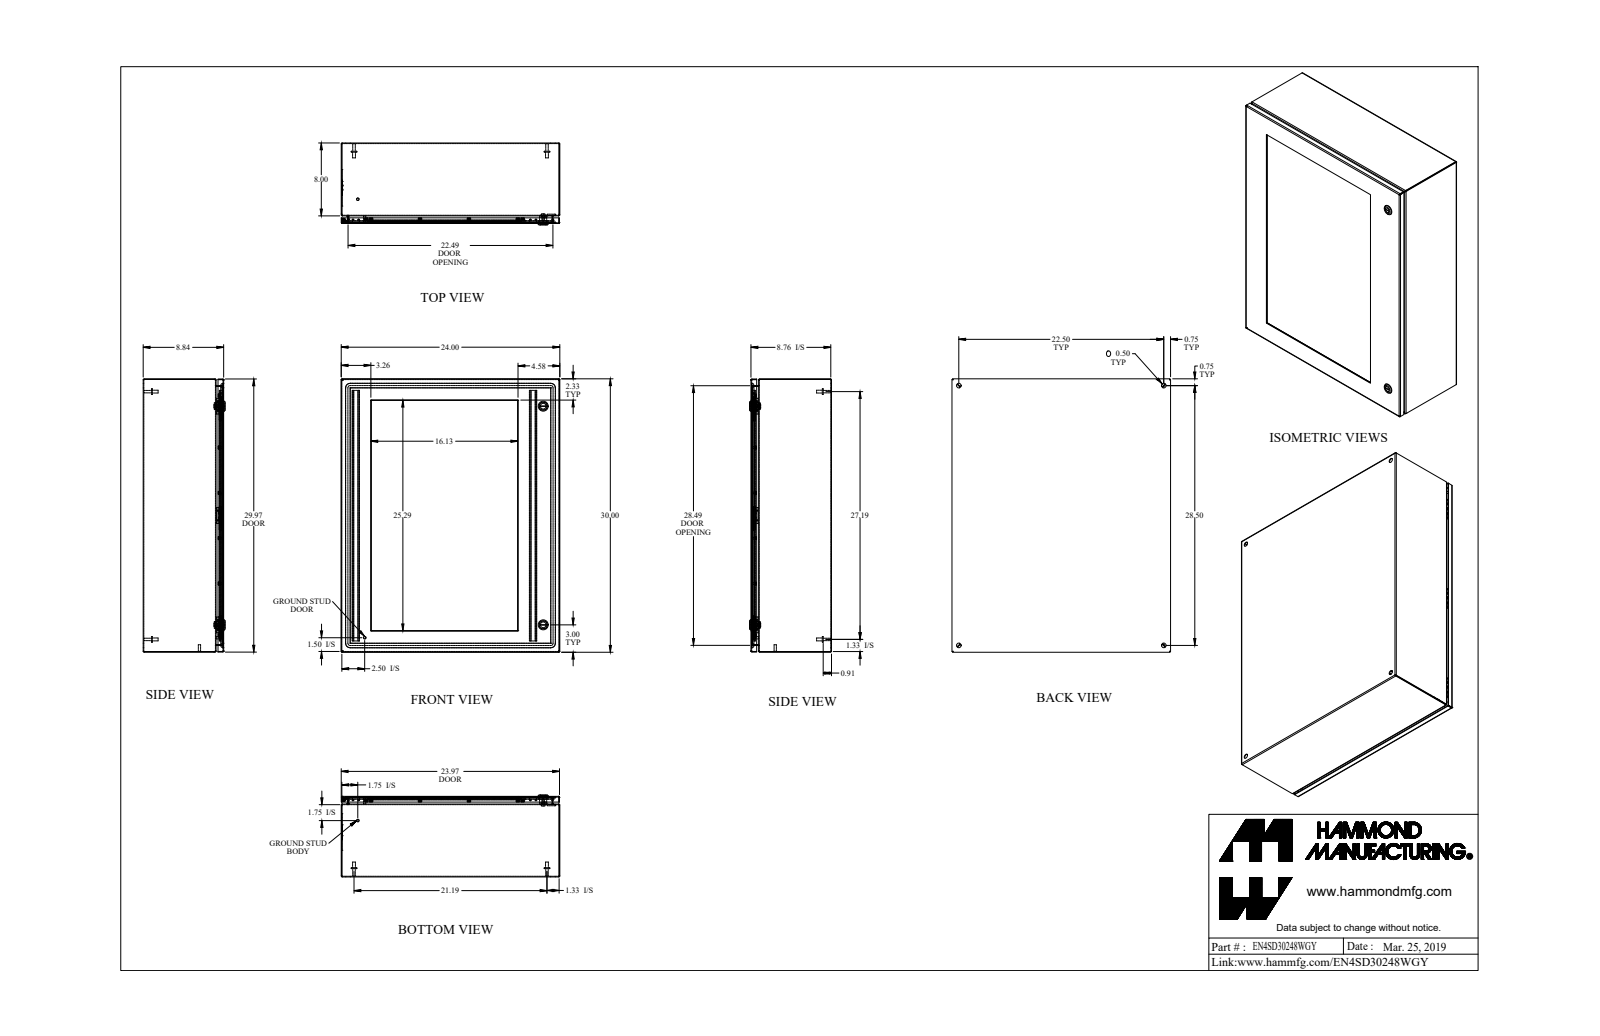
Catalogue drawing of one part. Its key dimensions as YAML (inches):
part_name: "EN4SD30248WGY_Default"
step_written_by: "SolidWorks 2019 (CONFIG_CONTROL_DESIGN)"
units: inches
bodies: {solids: 80, faces: 1652, planar: 833, cylindrical: 511, other: 308}
overall_size: [30, 24, 8.997]
volume: 281.4
surface_area: 5826
round_holes:
  - {diameter: 0.13, count: 20}
  - {diameter: 0.25, count: 20}
  - {diameter: 0.5, count: 4}
  - {diameter: 0.232, count: 2}
  - {diameter: 0.625, count: 2}
  - {diameter: 0.785, count: 2}
  - {diameter: 0.172, count: 1}
  - {diameter: 0.24, count: 1}
  - {diameter: 0.242, count: 1}
round_bosses_or_shafts:
  - {diameter: 0.226, count: 21}
  - {diameter: 0.368, count: 20}
  - {diameter: 0.164, count: 20}
  - {diameter: 0.625, count: 4}
  - {diameter: 0.313, count: 4}
  - {diameter: 0.27, count: 4}
  - {diameter: 1.1, count: 2}
  - {diameter: 0.525, count: 2}
partial_cylinders:
  - {radius: 0.036, count: 20}
  - {radius: 0.108, count: 20}
  - {radius: 0.043, count: 12}
  - {radius: 0.081, count: 12}
  - {radius: 0.125, count: 12}
  - {radius: 0.382, count: 12}
  - {radius: 19.003, count: 8}
  - {radius: 0.006, count: 6}
face_to_face_distances: [0.072, 8.765, 8.693, 8.443, 0.25, 8.515, 23.928, 29.928, 0.322, 8.837]
hole_center_spacings: [9.95, 19.822, 4.975, 17.144, 17.851, 5.372, 5.372, 14.925]
